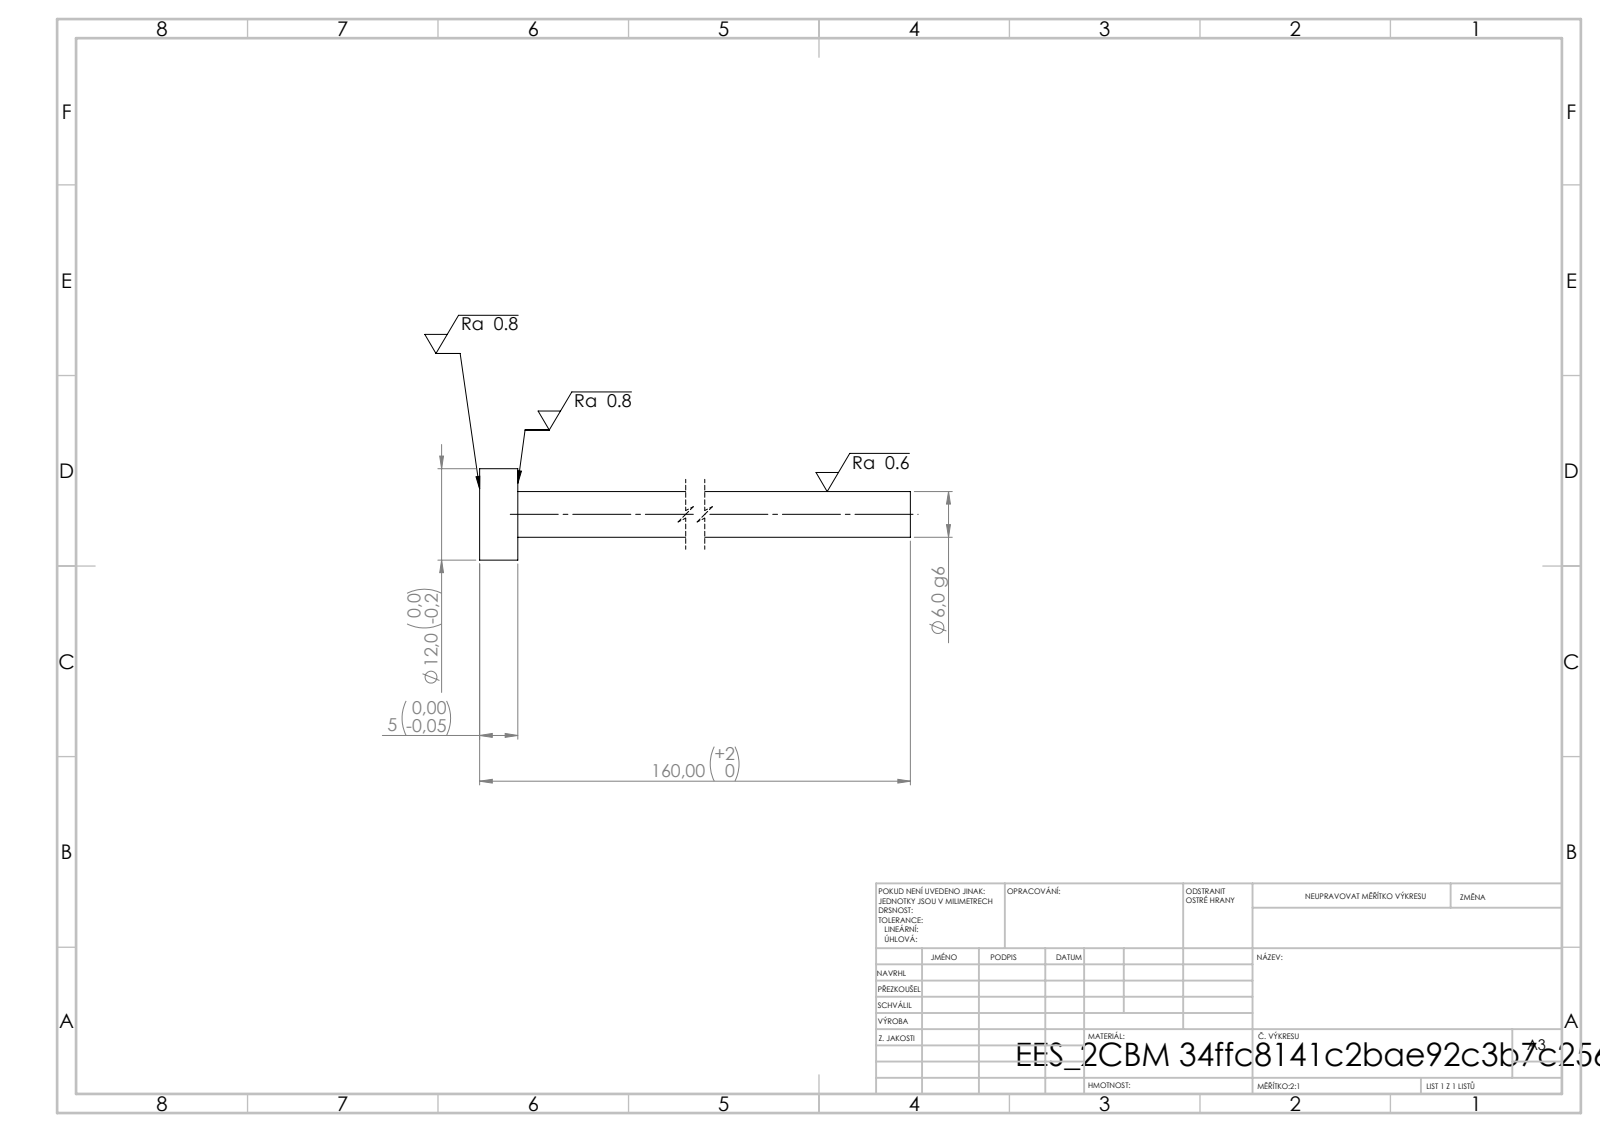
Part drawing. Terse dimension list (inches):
written by: SolidWorks 2019 (CONFIG_CONTROL_DESIGN)
unit: in
bodies: 1 solid, 7 faces (3 planar, 4 cylindrical, 0 other)
size: 6.299 × 0.472 × 0.472
volume: 0.302 in³; area: 5.171 in²
bosses: 1× ⌀0.472, 1× ⌀0.236
face distances: 0.197, 6.299, 6.102
